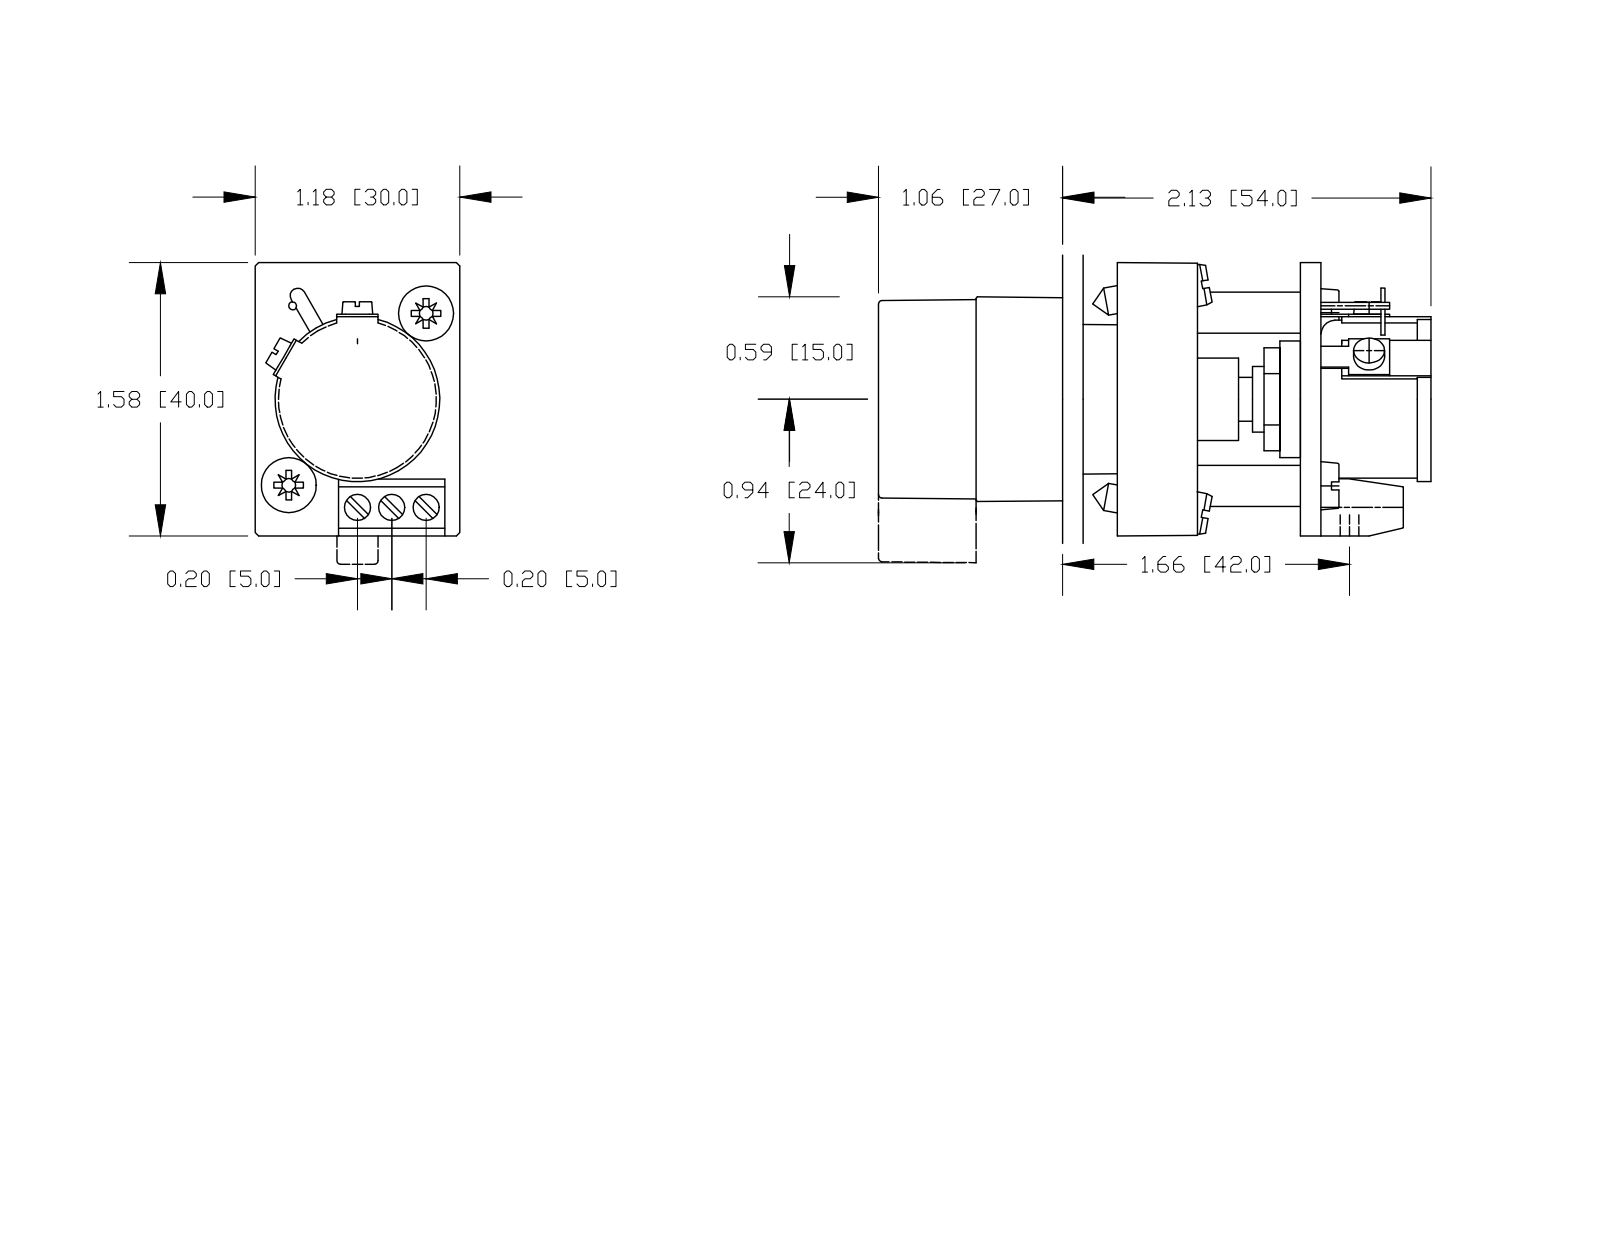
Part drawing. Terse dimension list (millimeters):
name: ECX2300-10K POT; GCX2300-10K OPERATOR; ECX2300-10K
written by: SolidWorks 2016 (AUTOMOTIVE_DESIGN)
unit: mm
bodies: 12 solids, 358 faces (194 planar, 141 cylindrical, 23 other)
size: 78.3 × 40.2 × 29.9
volume: 35 510 mm³; area: 22 690 mm²
holes: 3× ⌀3, 2× ⌀3.1, 2× ⌀3.3, 1× ⌀5, 1× ⌀12, 1× ⌀22.3, 1× ⌀22.6, 1× ⌀26
bosses: 2× ⌀6, 2× ⌀4, 1× ⌀29.8, 1× ⌀25.5, 1× ⌀24, 1× ⌀23, 1× ⌀21.7, 1× ⌀19.8
rounds: 24× R1.5, 12× R1, 12× R3.1, 12× R4, 6× R1, 2× R3.3, 1× R2.9, 1× R10
face distances: 3.4, 36.2, 32.8, 12, 17.9, 14.5, 18.3, 0.8, 12, 17.9
hole spacings: 5, 10, 15.7, 16.6, 18.8
